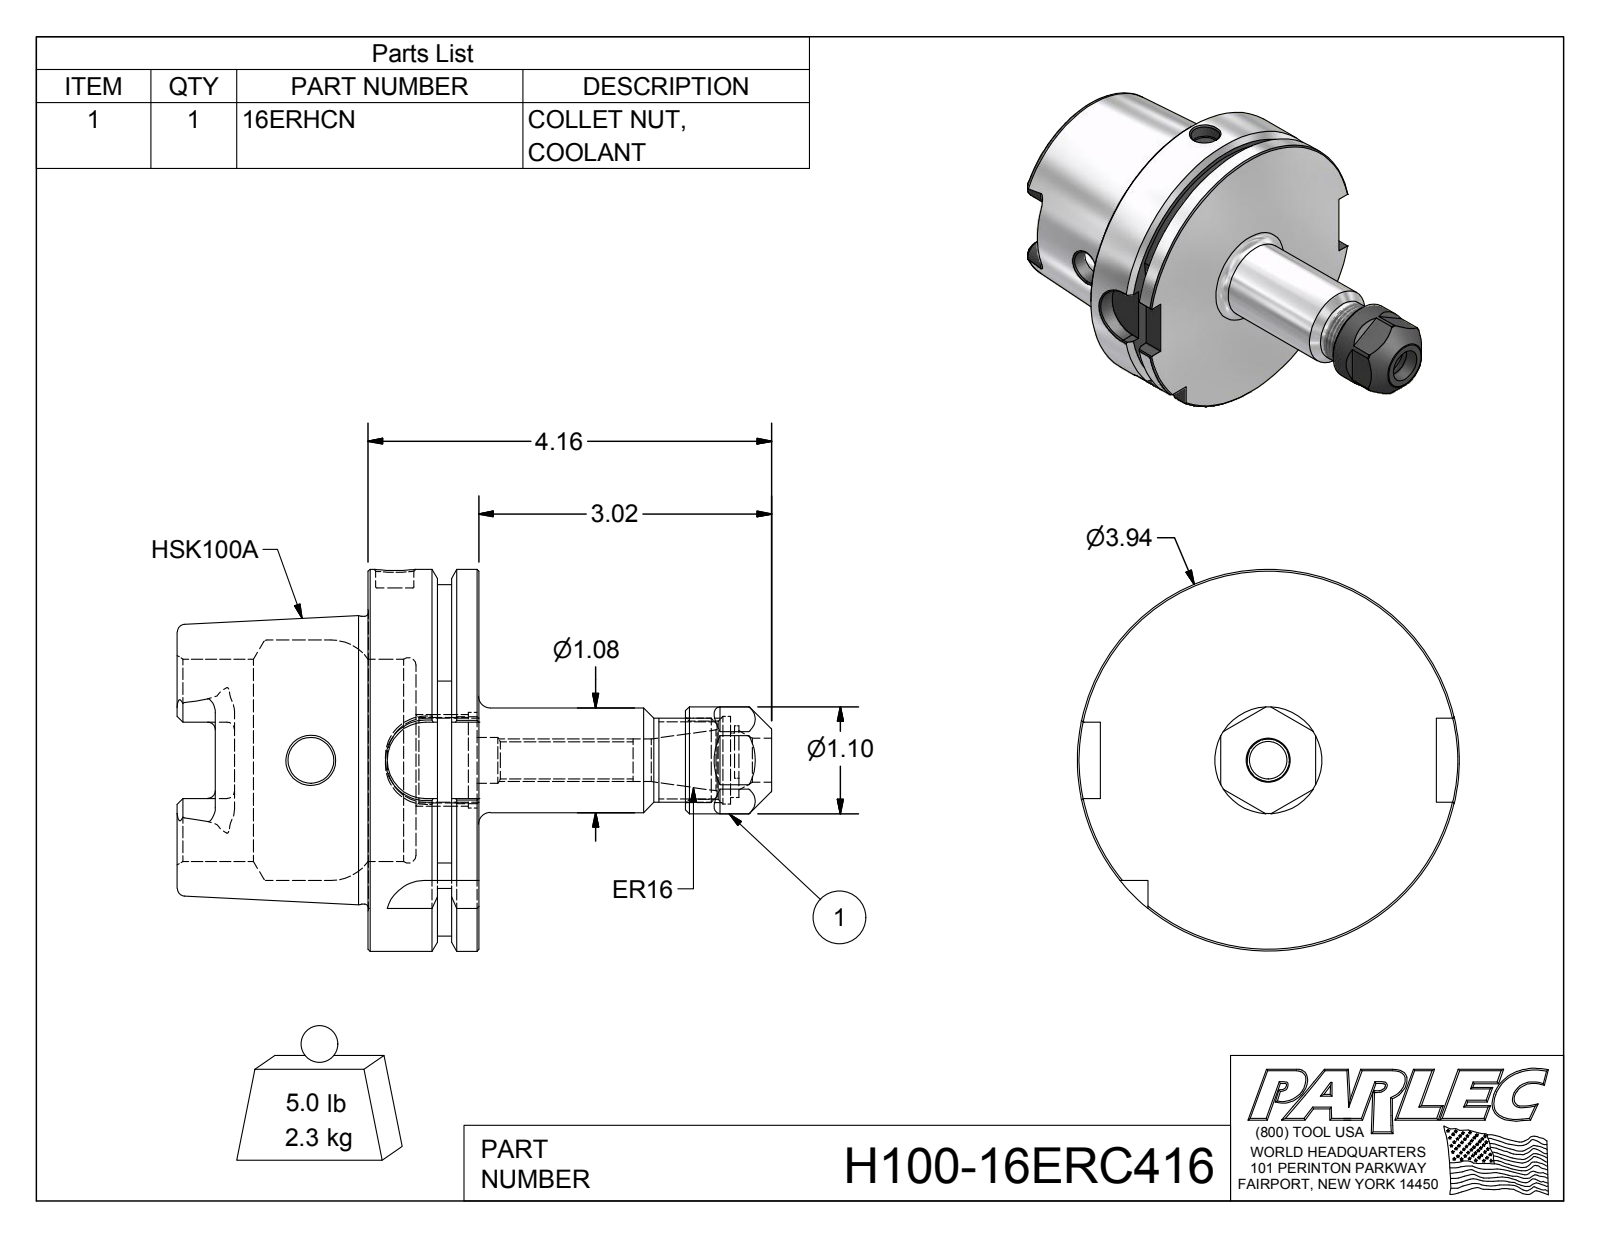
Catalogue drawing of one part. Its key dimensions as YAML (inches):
part_name: "H100-16ERC416; H100-16ER4-1; 16ERHCN"
step_written_by: "Autodesk Inventor 2012 (AUTOMOTIVE_DESIGN)"
units: inches
bodies: {solids: 2, faces: 165, planar: 61, cylindrical: 42, other: 62}
overall_size: [6.129, 3.937, 3.937]
volume: 17.5
surface_area: 94.06
round_holes:
  - {diameter: 0.472, count: 2}
  - {diameter: 0.383, count: 1}
  - {diameter: 0.394, count: 1}
  - {diameter: 0.44, count: 1}
  - {diameter: 0.453, count: 1}
  - {diameter: 0.472, count: 1}
  - {diameter: 0.661, count: 1}
  - {diameter: 0.807, count: 1}
  - {diameter: 0.881, count: 1}
  - {diameter: 0.906, count: 1}
  - {diameter: 0.985, count: 1}
  - {diameter: 2.087, count: 1}
round_bosses_or_shafts:
  - {diameter: 3.937, count: 1}
  - {diameter: 2.967, count: 1}
  - {diameter: 1.102, count: 1}
  - {diameter: 1.08, count: 1}
  - {diameter: 0.866, count: 1}
partial_cylinders:
  - {radius: 0.079, count: 6}
  - {radius: 0.192, count: 4}
  - {radius: 0.394, count: 4}
  - {radius: 0.354, count: 1}
  - {radius: 1.811, count: 1}
face_to_face_distances: [1.142, 0.492, 0.65, 1.969, 2.461, 3.11, 2.83, 0.861, 0.369, 0.28]
hole_center_spacings: [0.051]
